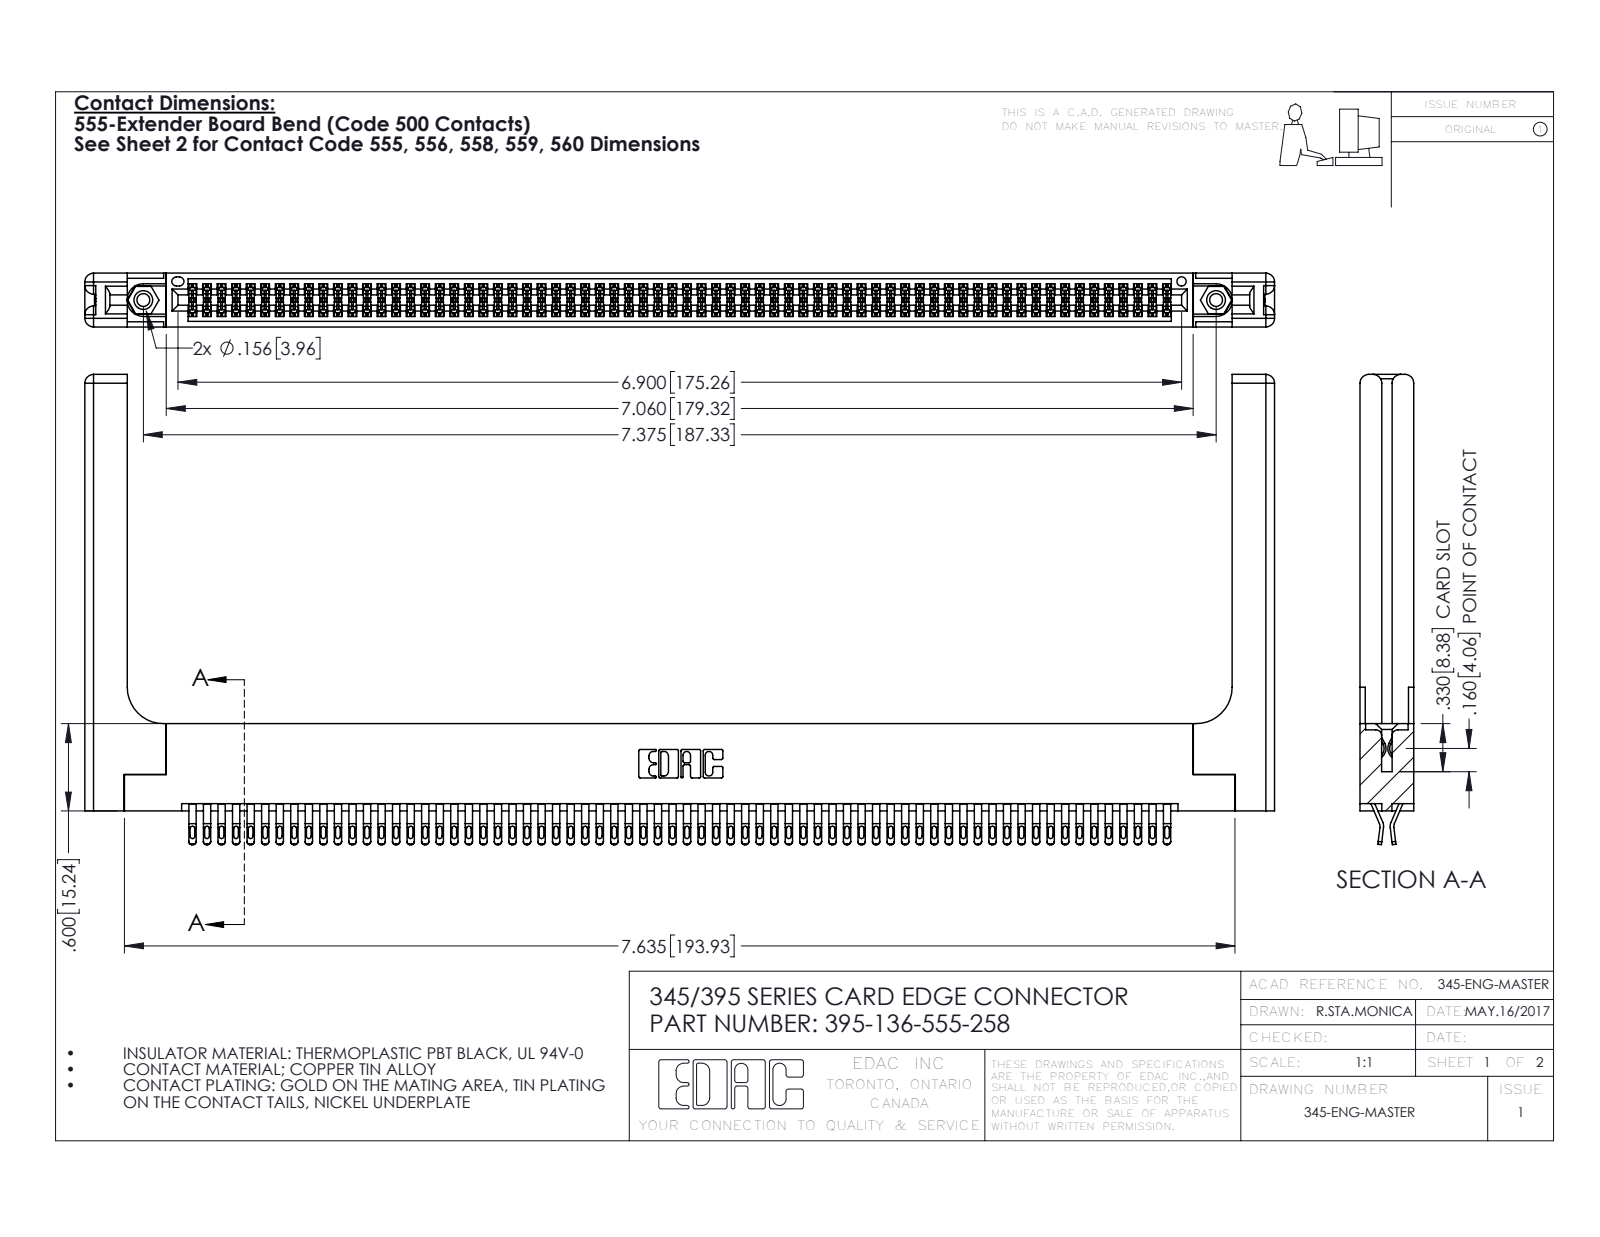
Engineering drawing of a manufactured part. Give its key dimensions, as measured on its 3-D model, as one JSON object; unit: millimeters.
{"part_name": "345 Part_Flush Mounting Lugs - 0.156 Dia-TH; 345-220-058_345-220-058; 345-292-001_555 Tail; 395-136-555-258 (+1 more)", "step_written_by": "SolidWorks 2016 (CONFIG_CONTROL_DESIGN)", "units": "millimeters", "bodies": {"solids": 141, "faces": 7998, "planar": 4444, "cylindrical": 3494, "other": 60}, "overall_size": [207.7, 82.1, 9.4], "volume_mm3": 29280, "surface_area_mm2": 37700, "round_holes": [[2.3, 2], [3.2, 2], [4, 2], [1.6, 1]], "round_bosses_or_shafts": [[3.9, 2]], "partial_cylinders_radius": [[0.4, 340], [0.5, 272], [0.2, 204], [0.3, 22], [1.5, 16], [0.2, 6], [0.8, 6], [0.7, 3]], "face_to_face_distances": [1.8, 7.6, 9.4, 0.6, 5.1, 2.5, 6.9, 5.7, 3.8, 3.8], "hole_center_spacings": [6.9, 181.3, 187.3]}
